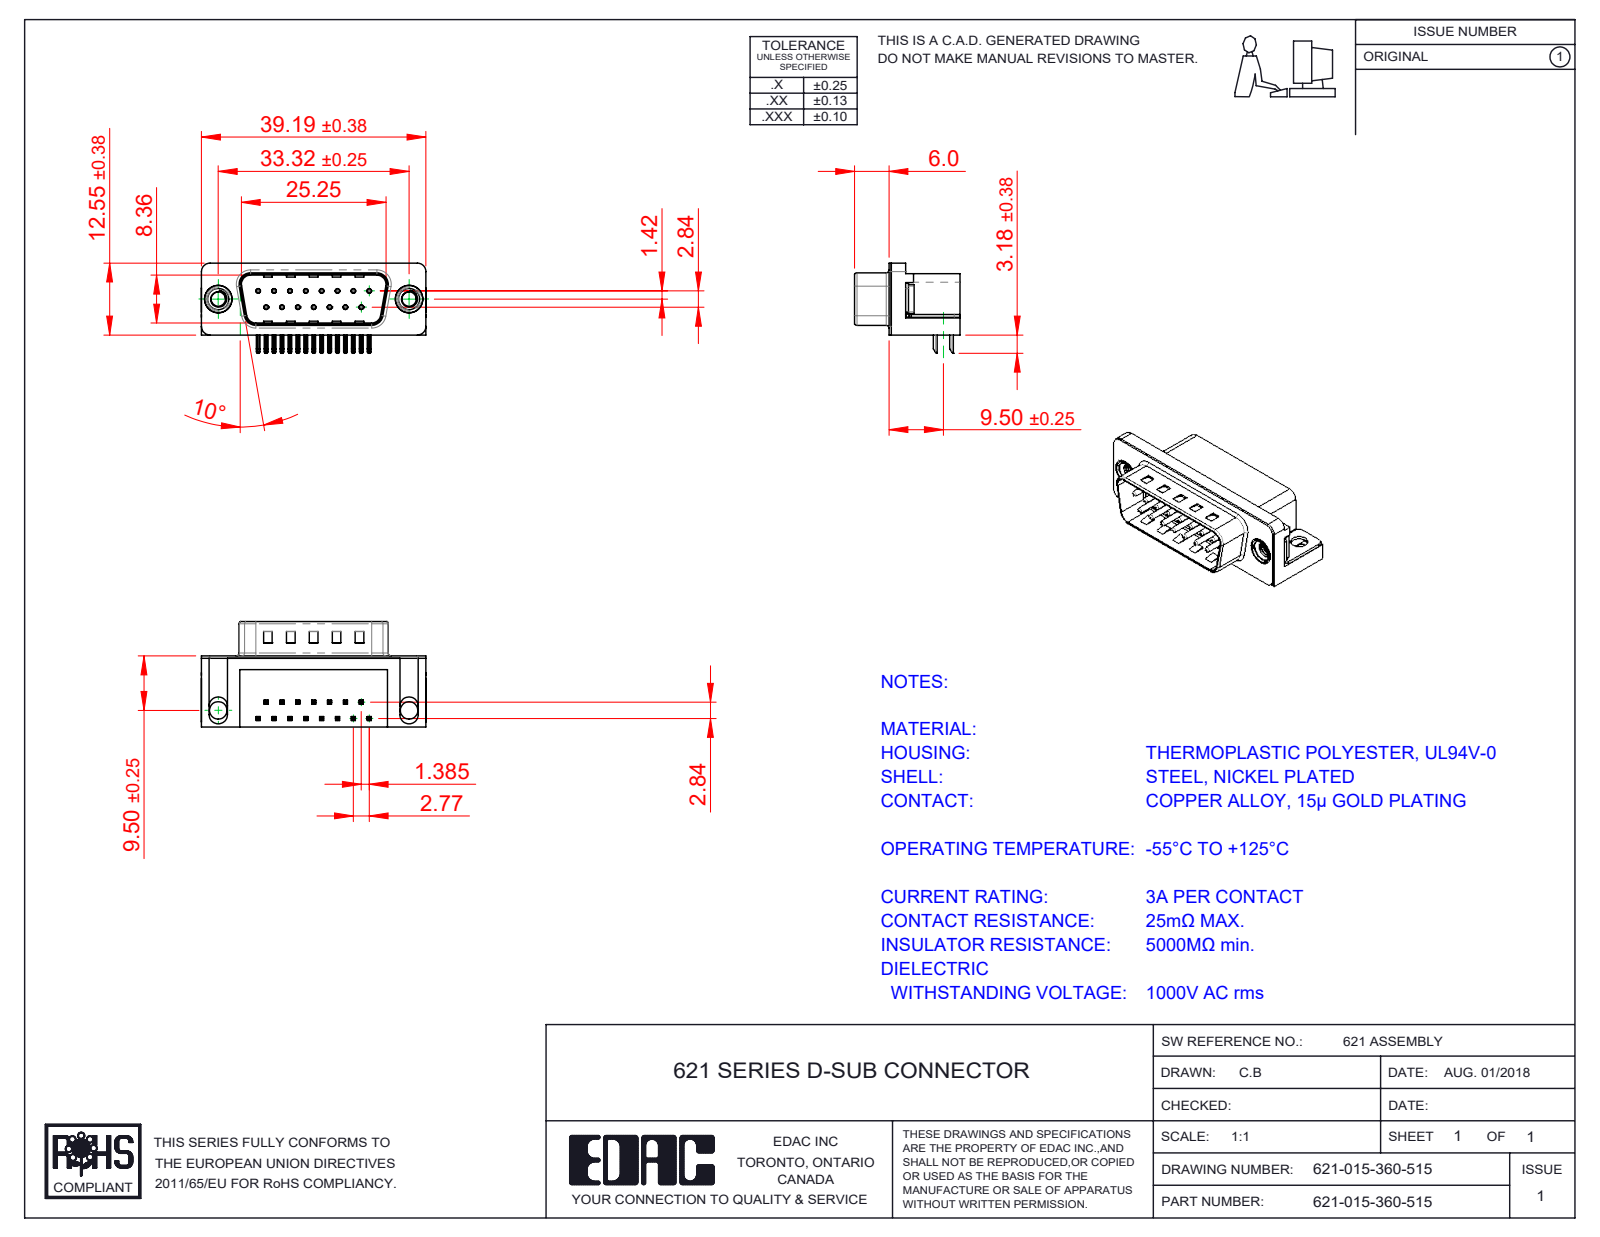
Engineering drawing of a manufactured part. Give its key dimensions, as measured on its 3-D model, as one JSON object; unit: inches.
{"part_name": "621 Housing_15 Socket; 621 Shell_15 Socket; 621 M3 Threaded Rivet; 621 Contact Bottom (+3 more)", "step_written_by": "SolidWorks 2016 (CONFIG_CONTROL_DESIGN)", "units": "inches", "bodies": {"solids": 21, "faces": 1475, "planar": 891, "cylindrical": 449, "other": 135}, "overall_size": [1.544, 0.724, 0.619], "volume_in3": 0.269, "surface_area_in2": 8.742, "round_holes": [[0.014, 15], [0.031, 15], [0.098, 2], [0.12, 2], [0.157, 2], [0.189, 2], [0.197, 2]], "round_bosses_or_shafts": [[0.03, 15], [0.193, 2], [0.187, 2], [0.154, 2]], "partial_cylinders_radius": [[0.01, 68], [0.005, 30], [0.039, 16], [0.02, 9], [0.063, 8], [0.059, 6], [0.035, 4], [0.079, 4]], "face_to_face_distances": [0.016, 0.472, 0.407, 0.083, 0.412, 0.488, 0.067, 0.428, 0.345, 0.114], "hole_center_spacings": [0.124, 0.109, 0.218, 0.327, 0.436, 0.198, 0.198, 0.294]}
